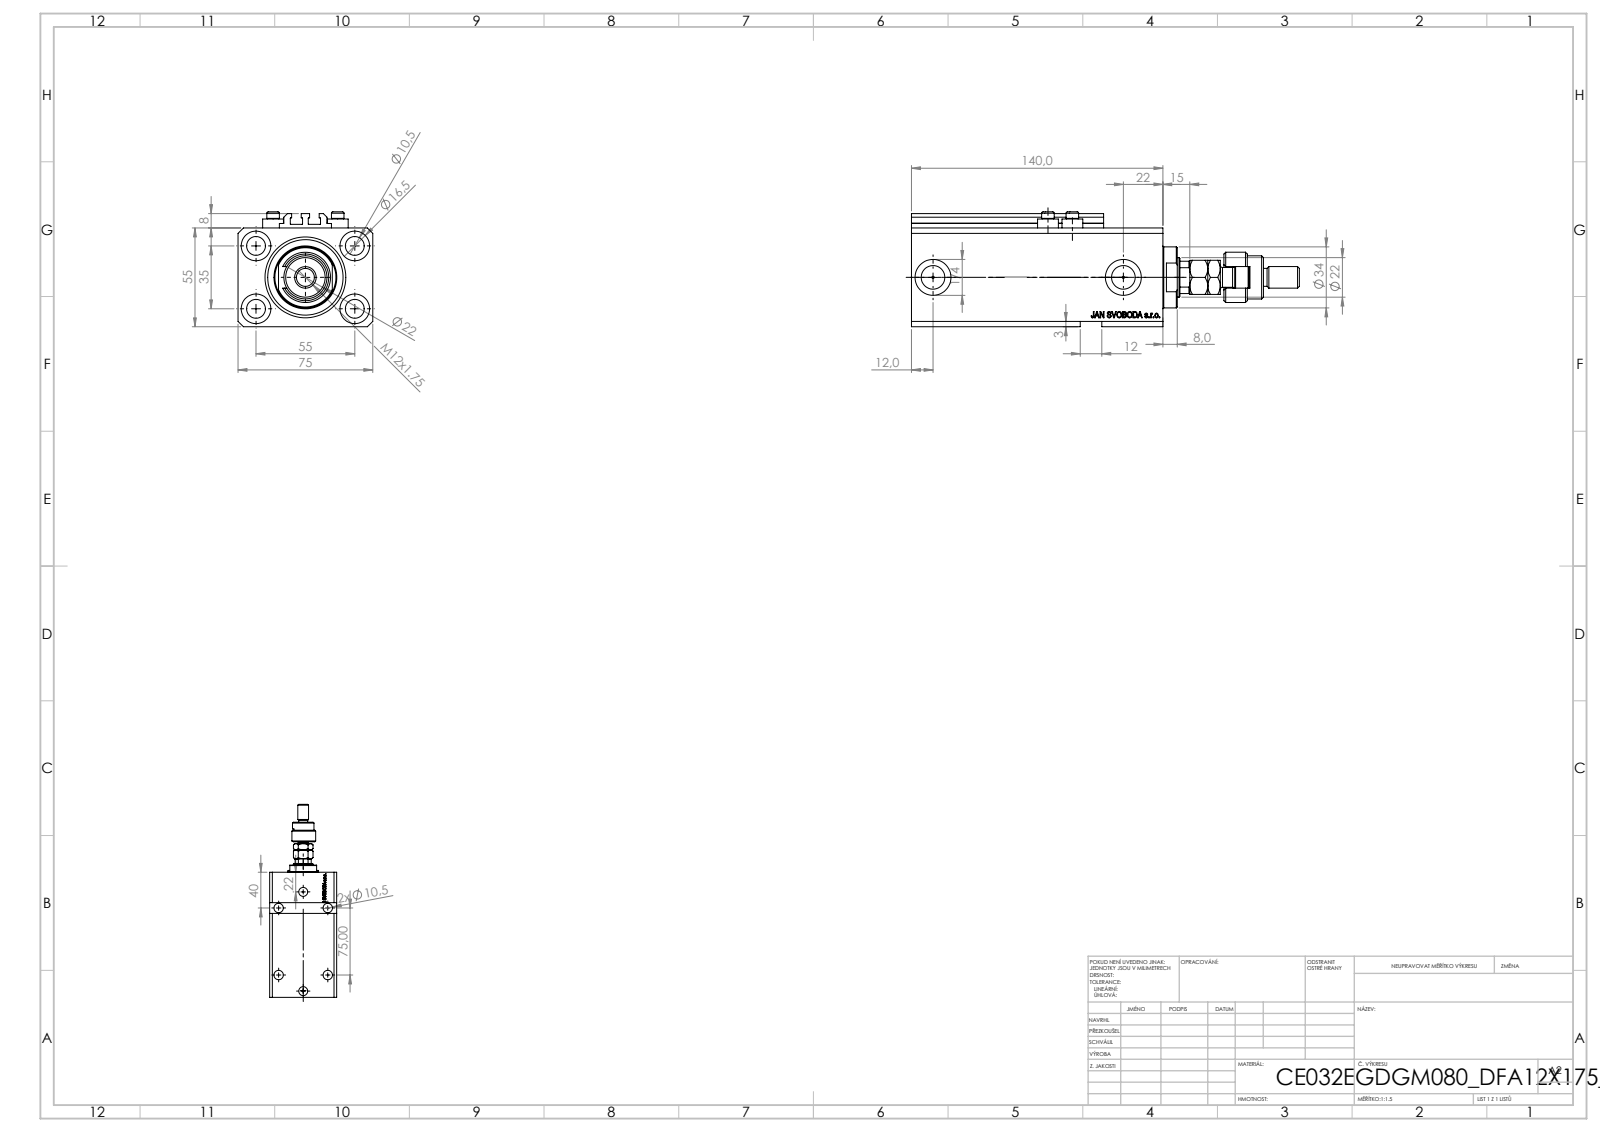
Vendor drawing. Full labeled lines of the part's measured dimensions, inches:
Part name (STEP PRODUCT): V250CE_VC_E; MFA; V250CE_E_Body; ALLEN BOLT V250CE (+2 more)
STEP written by: SolidWorks 2019 (CONFIG_CONTROL_DESIGN)
Units: inches
Bodies: 10 solids, 1185 faces (546 planar, 171 cylindrical, 468 other)
Overall size (bounding box): 8.504 × 2.953 × 2.52
Volume: 30.48 in³ · Surface area: 191.5 in²
Round holes (diameter × count): ⌀0.413 ×9, ⌀0.049 ×4, ⌀0.157 ×4, ⌀0.65 ×4, ⌀0.394 ×2, ⌀0.518 ×2, ⌀0.787 ×2, ⌀0.866 ×1, ⌀1.26 ×1, ⌀1.772 ×1
Round bosses / shafts (diameter × count): ⌀0.457 ×4, ⌀0.276 ×4, ⌀1.339 ×1, ⌀1.102 ×1, ⌀0.945 ×1, ⌀0.709 ×1, ⌀0.472 ×1, ⌀0.433 ×1
Partial cylindrical surfaces — rounded edges, fillets, slot ends (radius × count): R0.008 ×10, R0.384 ×1, R0.413 ×1
Main face-to-face distances: 2.165, 2.953, 0.591, 0.39, 5.512, 0.315, 4.921, 0.118, 2.244, 4.531
Hole centre spacings: 1.283, 1.294, 2.165, 3.818, 0.535, 0.555, 1.016, 1.283
